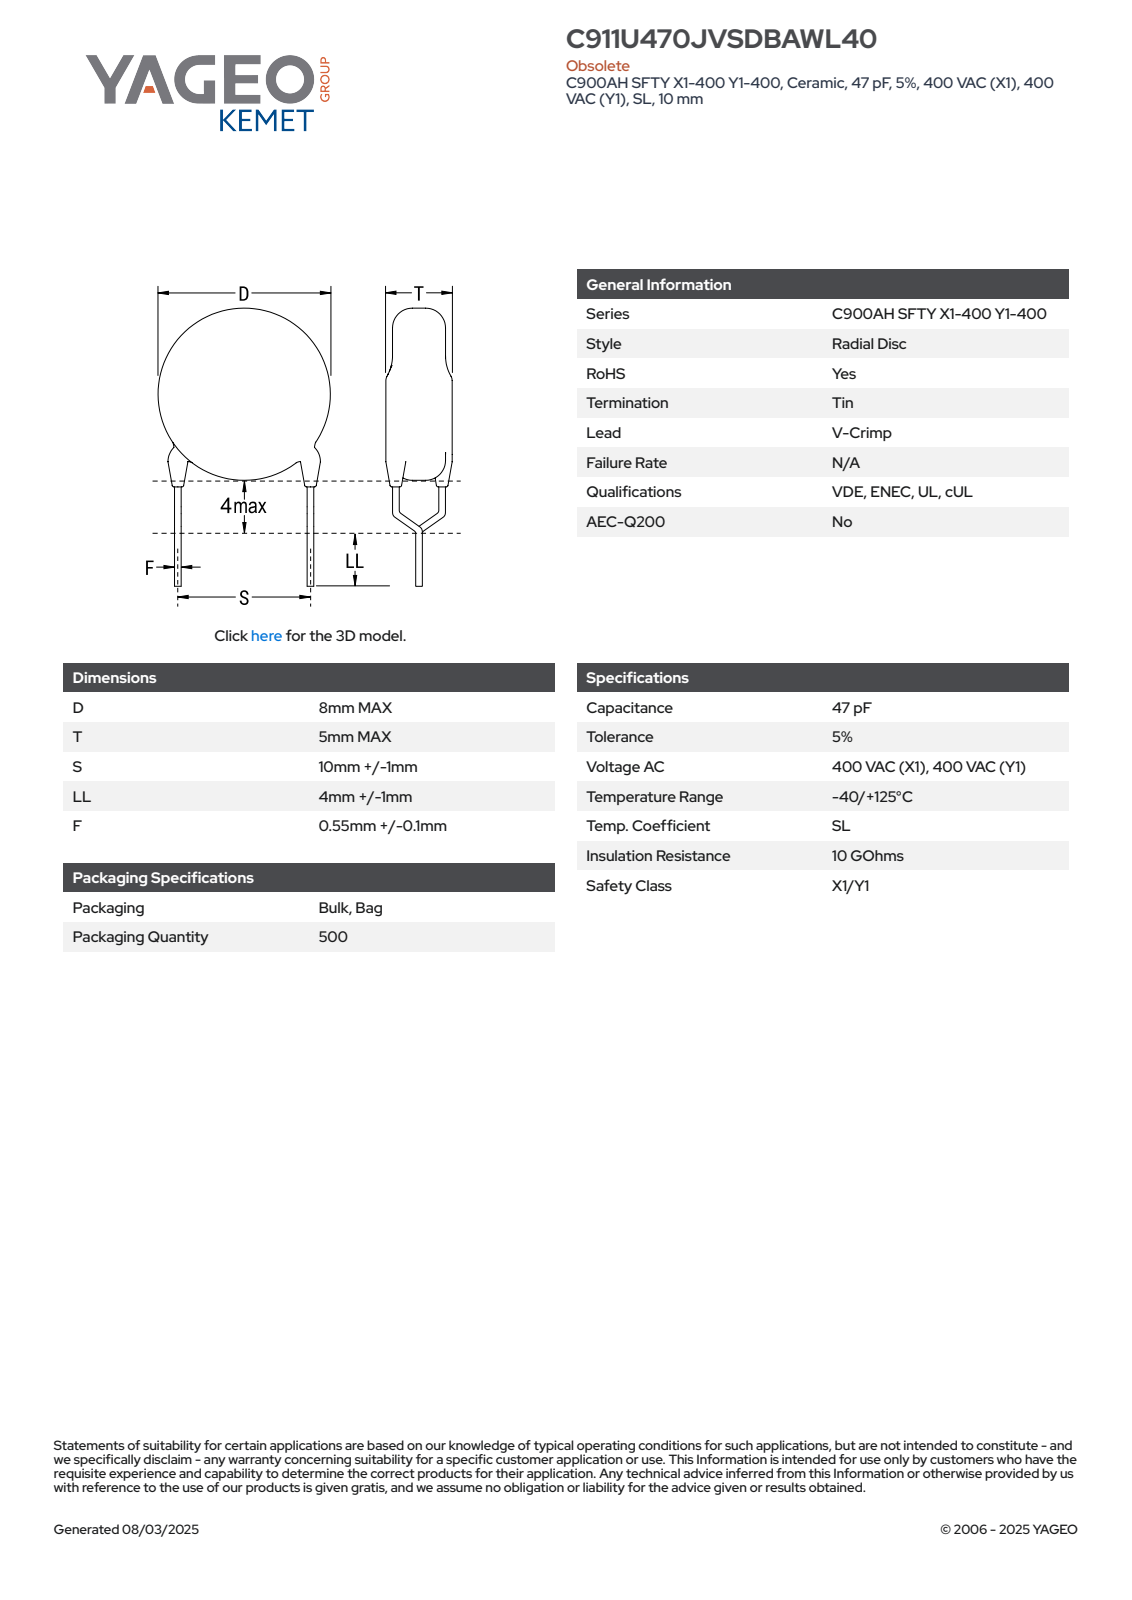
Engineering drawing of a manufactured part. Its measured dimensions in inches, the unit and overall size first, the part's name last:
Units: inches
Overall size (bounding box): 0.661 × 0.419 × 0.197
Round bosses / shafts (diameter × count): ⌀0.026 ×6, ⌀0.315 ×1
Main face-to-face distances: 0.197, 0.311, 0.041, 0.524, 0.213, 0.483, 0.172, 0.033, 0.018, 0.015
Volume: 0.015 in³ · Surface area: 0.409 in²
Bodies: 5 solids, 93 faces (65 planar, 16 cylindrical, 12 other)
Part name (STEP PRODUCT): CCD_VCC900_D8T5S10LL5F0.65
STEP written by: SolidWorks 2014 (AUTOMOTIVE_DESIGN)
